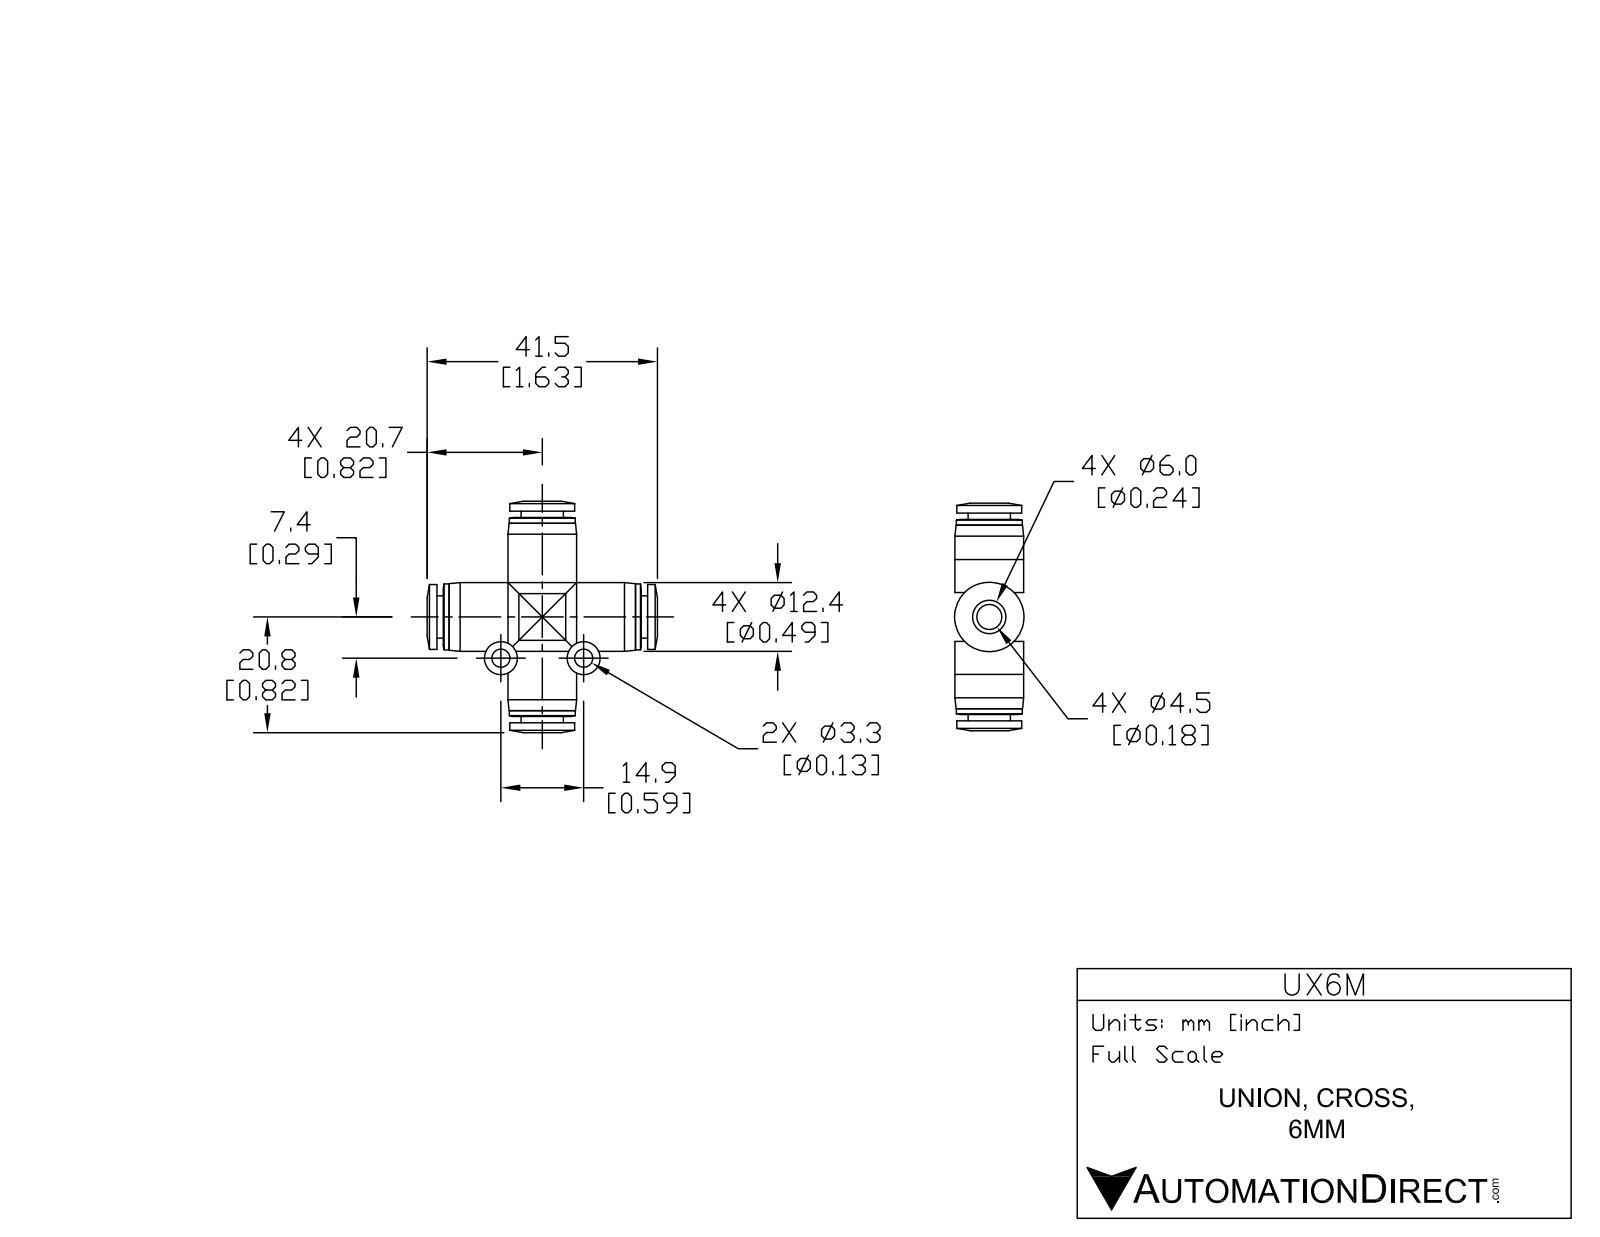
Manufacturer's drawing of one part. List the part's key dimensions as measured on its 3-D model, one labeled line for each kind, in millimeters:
Part name (STEP PRODUCT): UX6M
STEP written by: SolidWorks 2018 (AUTOMOTIVE_DESIGN)
Units: millimetres
Bodies: 1 solid, 124 faces (28 planar, 64 cylindrical, 32 other)
Overall size (bounding box): 42.1 × 41.4 × 12.5
Volume: 5 980 mm³ · Surface area: 5 456 mm²
Round holes (diameter × count): ⌀3.3 ×2, ⌀5 ×2, ⌀6.3 ×2
Round bosses / shafts (diameter × count): ⌀12.5 ×2, ⌀12 ×2, ⌀11.8 ×2, ⌀7.7 ×2, ⌀6 ×2
Partial cylindrical surfaces — rounded edges, fillets, slot ends (radius × count): R4.2 ×2
Main face-to-face distances: 1.1, 36.7, 37.3, 37.8, 38.5, 14.6, 13.5, 12.5, 35.5, 36.2
Hole centre spacings: 15
